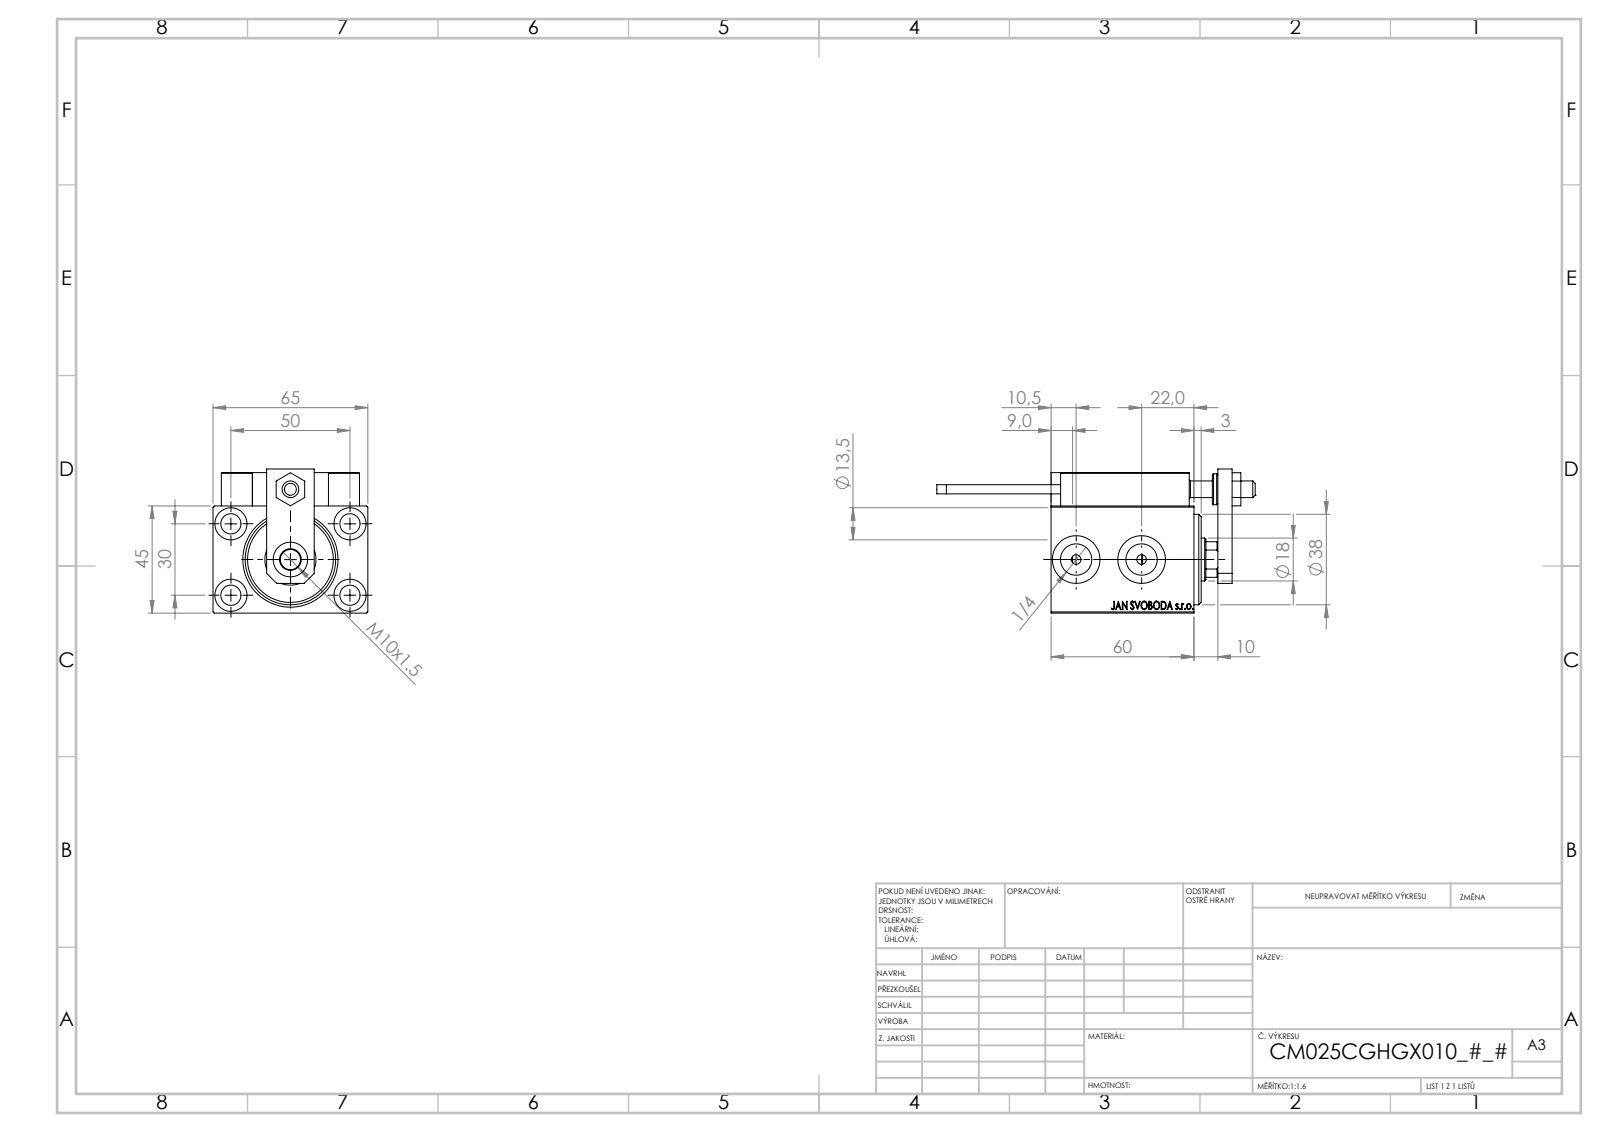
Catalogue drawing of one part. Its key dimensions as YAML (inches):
part_name: "Block; V450CM_C_VCP; V450CM_VC_B; V450CM_C_Body (+7 more)"
step_written_by: "SolidWorks 2019 (CONFIG_CONTROL_DESIGN)"
units: inches
bodies: {solids: 23, faces: 1283, planar: 561, cylindrical: 188, other: 534}
overall_size: [5.264, 2.559, 2.382]
volume: 12.07
surface_area: 101
round_holes:
  - {diameter: 0.157, count: 6}
  - {diameter: 0.315, count: 5}
  - {diameter: 0.335, count: 5}
  - {diameter: 0.126, count: 4}
  - {diameter: 0.531, count: 4}
  - {diameter: 0.197, count: 2}
  - {diameter: 0.518, count: 2}
  - {diameter: 0.787, count: 2}
  - {diameter: 0.276, count: 1}
  - {diameter: 0.571, count: 1}
  - {diameter: 0.709, count: 1}
  - {diameter: 0.846, count: 1}
round_bosses_or_shafts:
  - {diameter: 0.197, count: 2}
  - {diameter: 0.15, count: 2}
  - {diameter: 0.512, count: 1}
  - {diameter: 0.433, count: 1}
partial_cylinders:
  - {radius: 0.012, count: 30}
  - {radius: 0.118, count: 2}
  - {radius: 0.335, count: 1}
face_to_face_distances: [1.772, 0.394, 0.276, 2.323, 0.551, 0.118, 0.512, 2.559, 0.236, 0.354]
hole_center_spacings: [1.148, 0.448, 0.479, 0.787, 0.987, 1.138, 1.165, 1.169]
